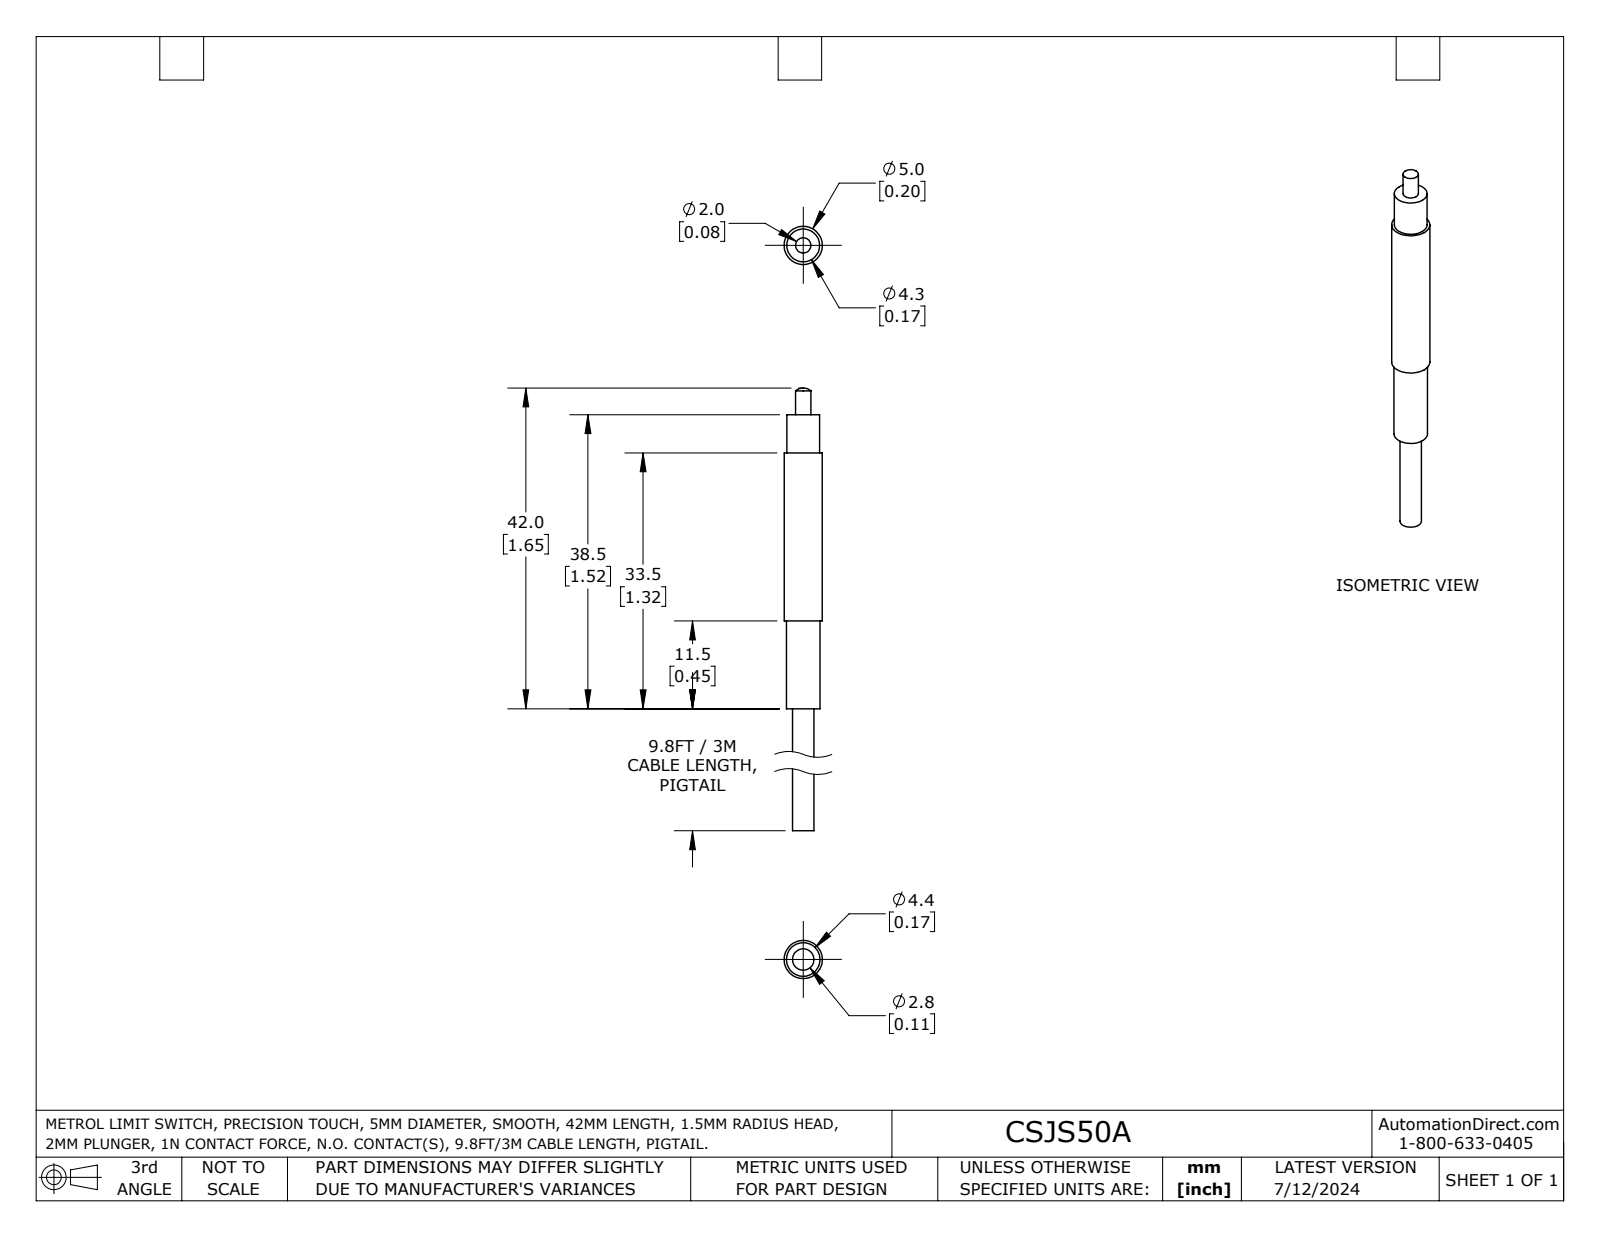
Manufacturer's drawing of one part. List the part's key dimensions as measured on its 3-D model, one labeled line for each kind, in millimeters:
Part name (STEP PRODUCT): CSJS50A
STEP written by: SolidWorks 2023 (AUTOMOTIVE_DESIGN)
Units: millimetres
Bodies: 1 solid, 17 faces (5 planar, 10 cylindrical, 2 other)
Overall size (bounding box): 56 × 5 × 5
Volume: 770 mm³ · Surface area: 755 mm²
Round bosses / shafts (diameter × count): ⌀5 ×1, ⌀4.4 ×1, ⌀4.3 ×1, ⌀2.8 ×1, ⌀2 ×1
Main face-to-face distances: 38.5, 14, 52.5, 47.5, 33.5, 5, 25.5, 11.5, 22, 27
